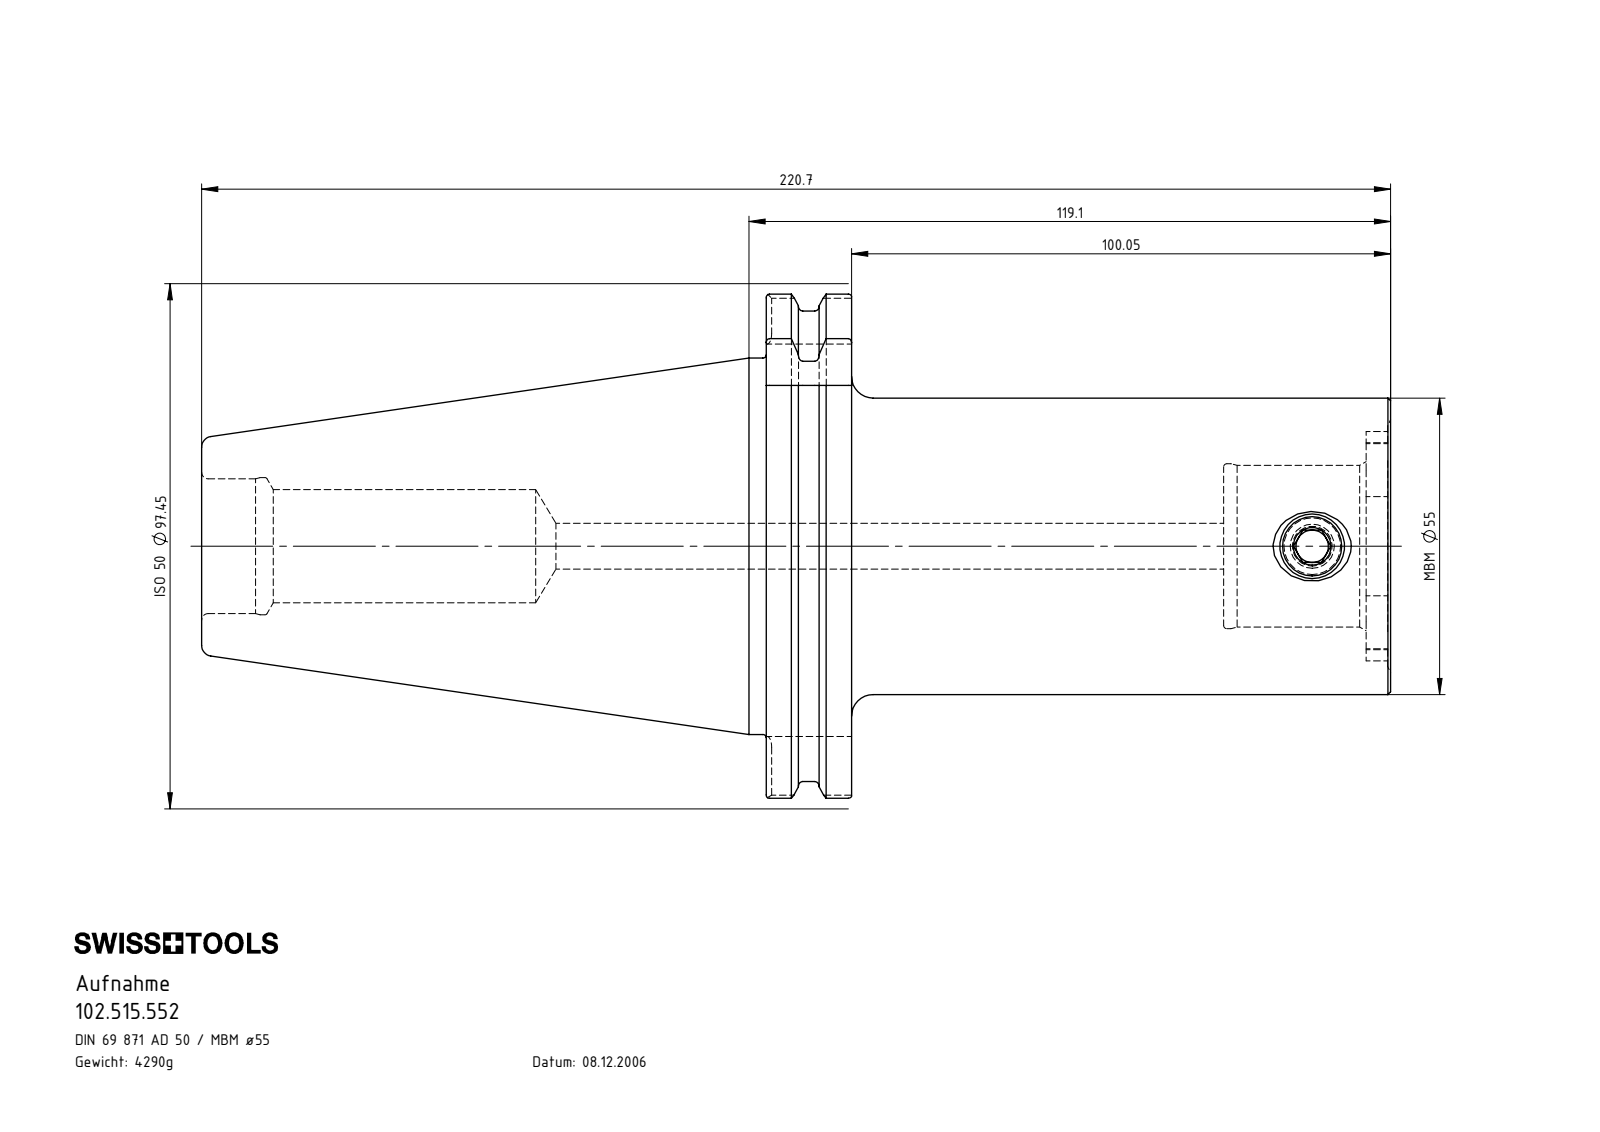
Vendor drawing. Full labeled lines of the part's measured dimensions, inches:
Part name (STEP PRODUCT): 102.515.552; MB5-ER1.001.017_A; SK5-MB5.K01.119_C
STEP written by: SolidWorks 2017 (CONFIG_CONTROL_DESIGN)
Units: inches
Bodies: 2 solids, 169 faces (55 planar, 50 cylindrical, 64 other)
Overall size (bounding box): 8.689 × 3.837 × 3.681
Volume: 33.35 in³ · Surface area: 99.18 in²
Round holes (diameter × count): ⌀0.236 ×1, ⌀0.335 ×1, ⌀0.433 ×1, ⌀0.827 ×1, ⌀0.984 ×1, ⌀1.002 ×1, ⌀1.181 ×1, ⌀1.205 ×1
Round bosses / shafts (diameter × count): ⌀3.583 ×1, ⌀2.75 ×1, ⌀2.165 ×1, ⌀0.472 ×1
Partial cylindrical surfaces — rounded edges, fillets, slot ends (radius × count): R0.079 ×8, R0.205 ×4, R0.728 ×1, R0.837 ×1, R1.919 ×1
Main face-to-face distances: 0.624, 3.343, 2.719, 4.563, 3.939, 1.22, 4.384, 3.76, 1.041, 0.179
